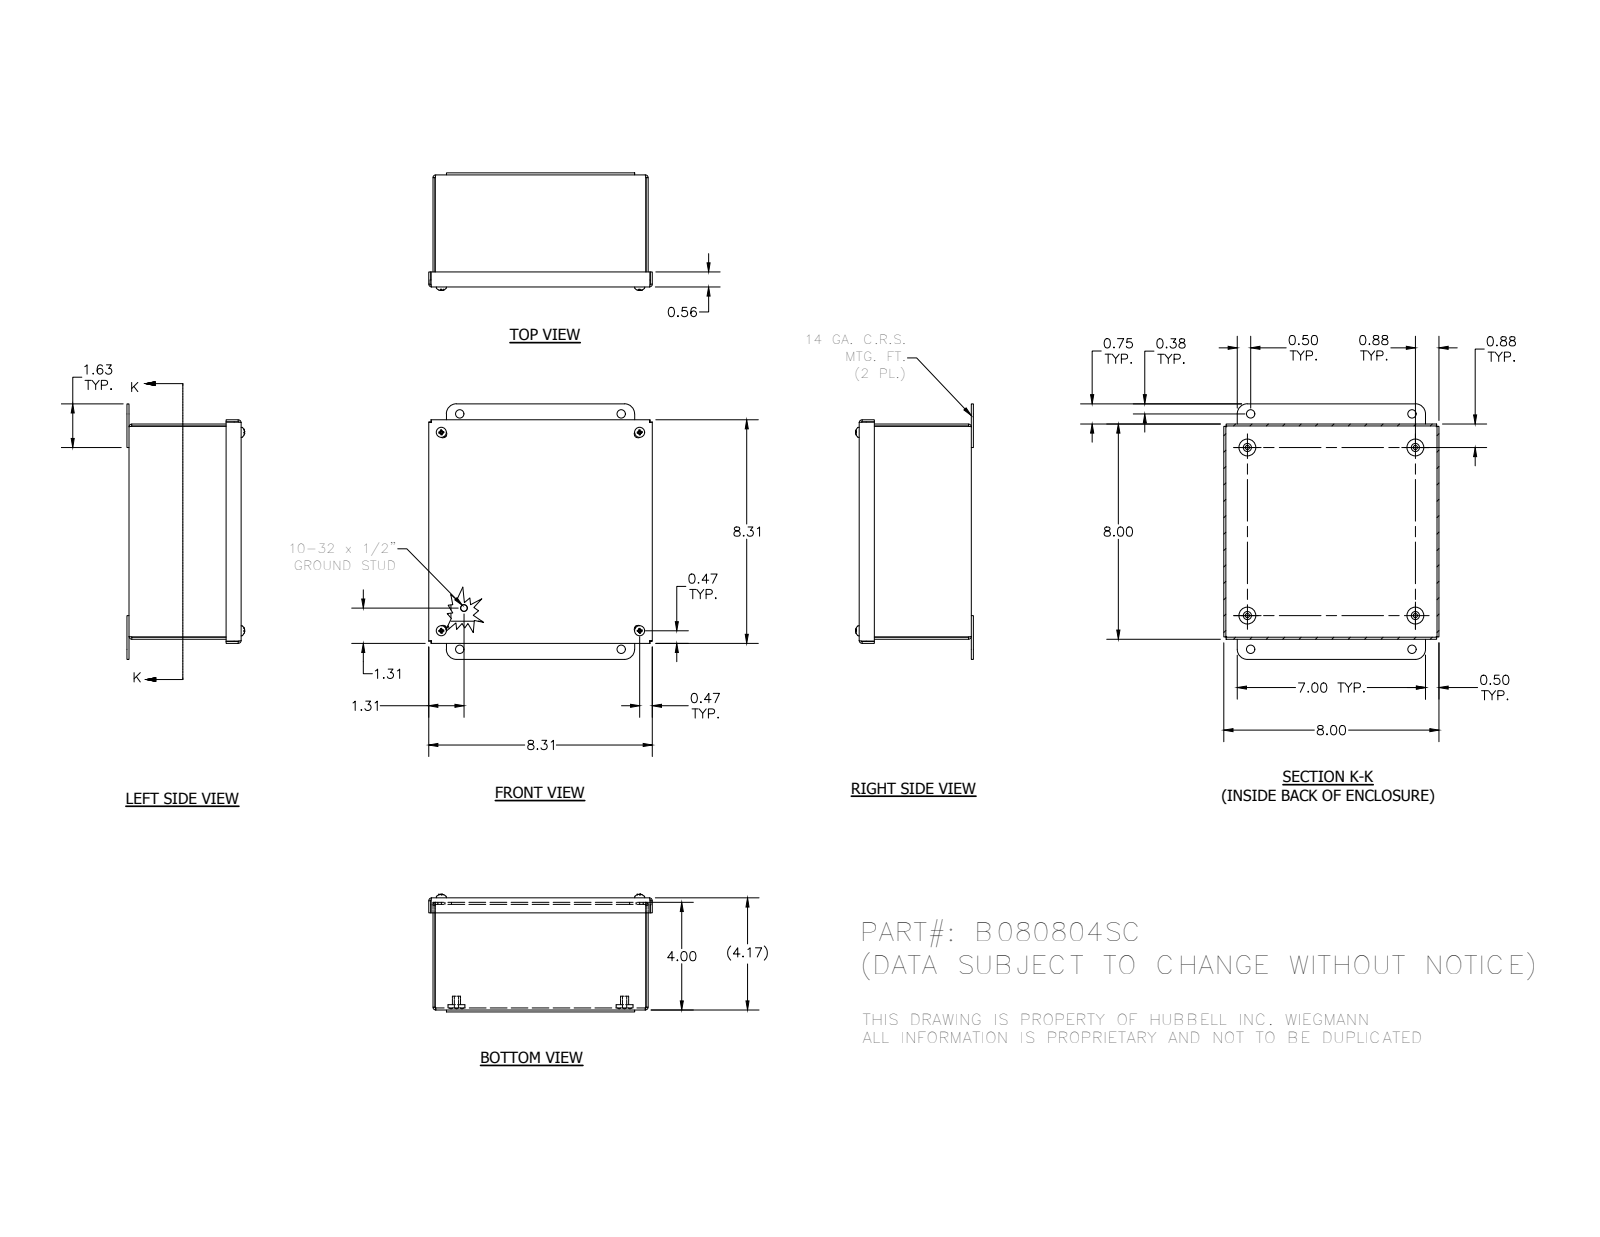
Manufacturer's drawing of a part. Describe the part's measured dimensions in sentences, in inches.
The part is named "B080804SC; 3483; 34984; B080804SCBKP (+6 more)". Its 3-D file was written by "Autodesk Inventor 2012 (AUTOMOTIVE_DESIGN)". It is 23 solids with 532 faces: 311 planar, 102 cylindrical and 119 other. Overall it measures 9.5 by 8.313 by 4.346 inches. Its volume is 26.7 cubic inches and its surface area 679.6 square inches. Round holes: 4 of diameter 0.145, 4 of diameter 0.156, 4 of diameter 0.196, 4 of diameter 0.278, 4 of diameter 0.281, 4 of diameter 0.31, 4 of diameter 0.313. Round bosses or shafts: 5 of diameter 0.19, 4 of diameter 0.625, 4 of diameter 0.453, 4 of diameter 0.406, 4 of diameter 0.373, 4 of diameter 0.3, 4 of diameter 0.248, 1 of diameter 0.25. Partial cylindrical surfaces (rounded edges, fillets, slot ends): 12 of radius 0.031, 12 of radius 0.105, 4 of radius 0.089, 4 of radius 0.375. The main face-to-face distances are 0.074, 4.094, 7.926, 4.168, 4.02, 7.852, 8, 0.187, 0.075, 0.149. The hole center spacings are 7.314, 6.835, 7.374, 7.375, 7.395, 10.343, 0.087, 6.722.
